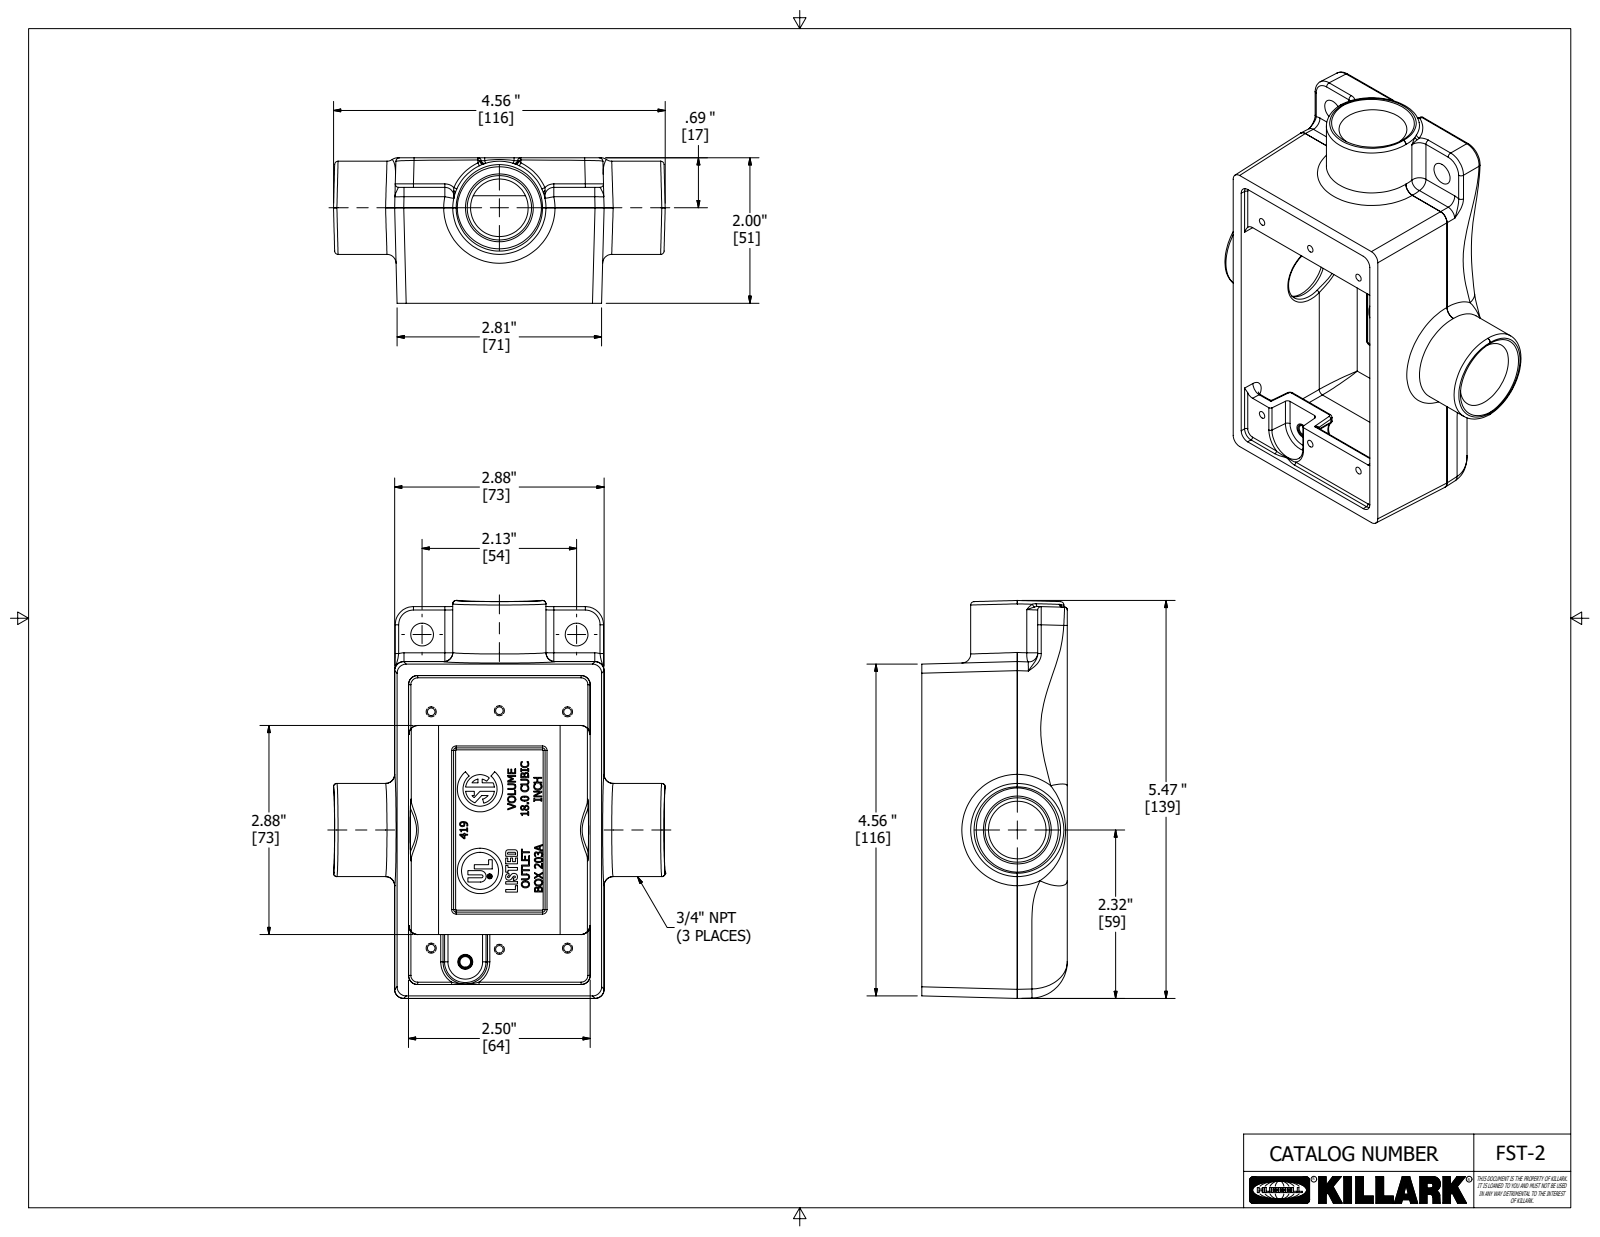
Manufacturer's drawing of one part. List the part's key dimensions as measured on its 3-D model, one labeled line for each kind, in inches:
Part name (STEP PRODUCT): 23862-3
STEP written by: Autodesk Inventor 2020 (AUTOMOTIVE_DESIGN)
Units: inches
Bodies: 1 solid, 1160 faces (563 planar, 169 cylindrical, 428 other)
Overall size (bounding box): 5.472 × 4.562 × 2.075
Volume: 9.679 in³ · Surface area: 100.7 in²
Round holes (diameter × count): ⌀0.104 ×6, ⌀0.792 ×2, ⌀0.069 ×1, ⌀0.145 ×1, ⌀0.625 ×1
Round bosses / shafts (diameter × count): ⌀1.281 ×1, ⌀0.509 ×1, ⌀0.058 ×1
Partial cylindrical surfaces — rounded edges, fillets, slot ends (radius × count): R0.031 ×33, R0.125 ×19, R0.047 ×15, R0.094 ×7, R0.062 ×5, R0.375 ×4, R0.013 ×2, R0.014 ×2
Main face-to-face distances: 2.656, 0.156, 1.75, 4.406, 0.031, 1.719, 1.594, 0.225, 1.906, 0.25
Hole centre spacings: 0.937, 3.397, 1.875, 3.25, 3.752, 0.153, 0.5, 0.505
